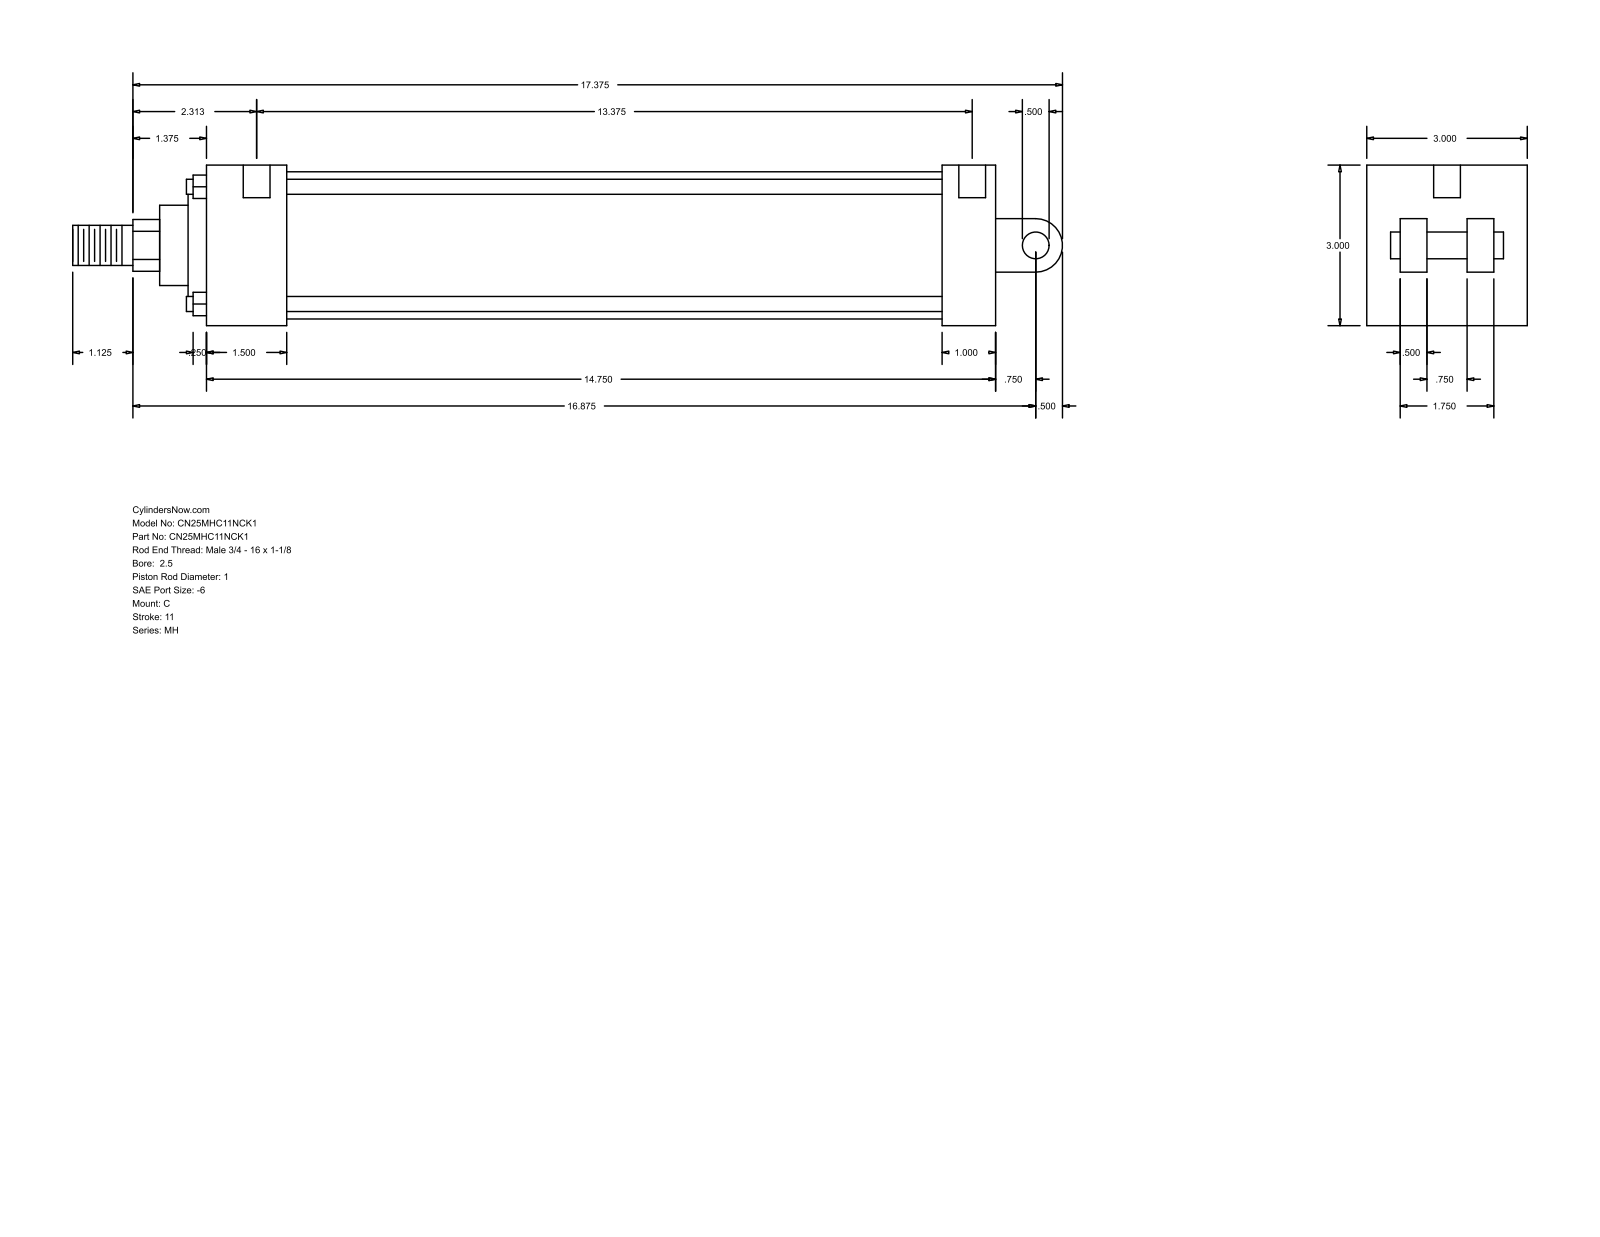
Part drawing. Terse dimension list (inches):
name: MH_C__0250_1
written by: GSSL Pune (CONFIG_CONTROL_DESIGN)
unit: in
bodies: 0 solids, 101 faces (71 planar, 30 cylindrical, 0 other)
size: 18.5 × 3 × 3
holes: 4× ⌀0.219, 2× ⌀0.5
bosses: 4× ⌀0.281, 1× ⌀2.75, 1× ⌀2.375, 1× ⌀1.5, 1× ⌀1, 1× ⌀0.75, 1× ⌀0.5
rounds: 1× R0.484, 1× R0.5
face distances: 3, 14.75, 1, 2.375, 0.625, 13.75, 1.5, 12.25, 13.25, 0.5
hole spacings: 13.687, 0.125, 0.187, 13.375, 13.5, 13.562
